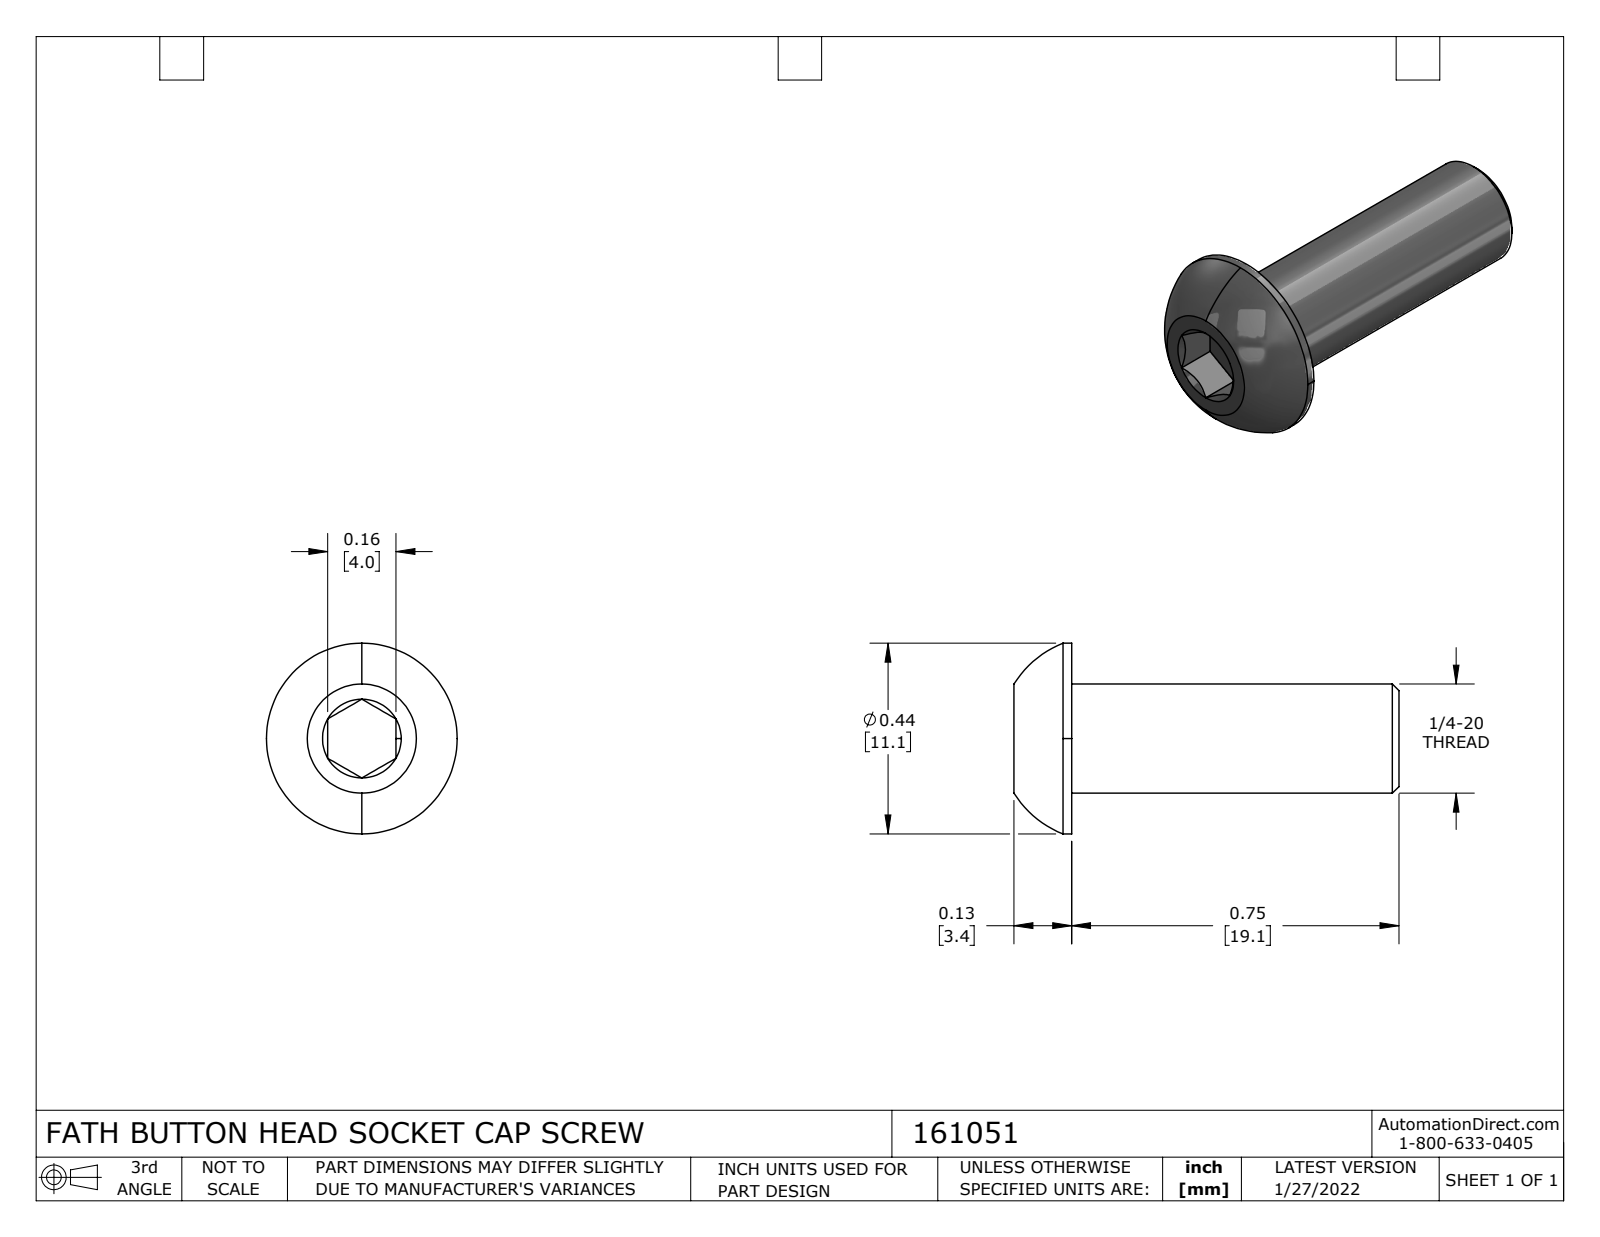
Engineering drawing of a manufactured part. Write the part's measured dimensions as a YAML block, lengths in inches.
part_name: "161051"
step_written_by: "SolidWorks 2021 (CONFIG_CONTROL_DESIGN)"
units: inches
bodies: {solids: 1, faces: 29, planar: 12, cylindrical: 4, other: 13}
overall_size: [0.882, 0.437, 0.437]
volume: 0.05
surface_area: 1.027
round_bosses_or_shafts:
  - {diameter: 0.437, count: 1}
  - {diameter: 0.25, count: 1}
face_to_face_distances: [0.75, 0.882, 0.132, 0.789, 0.039, 0.093, 0.156, 0.078]
